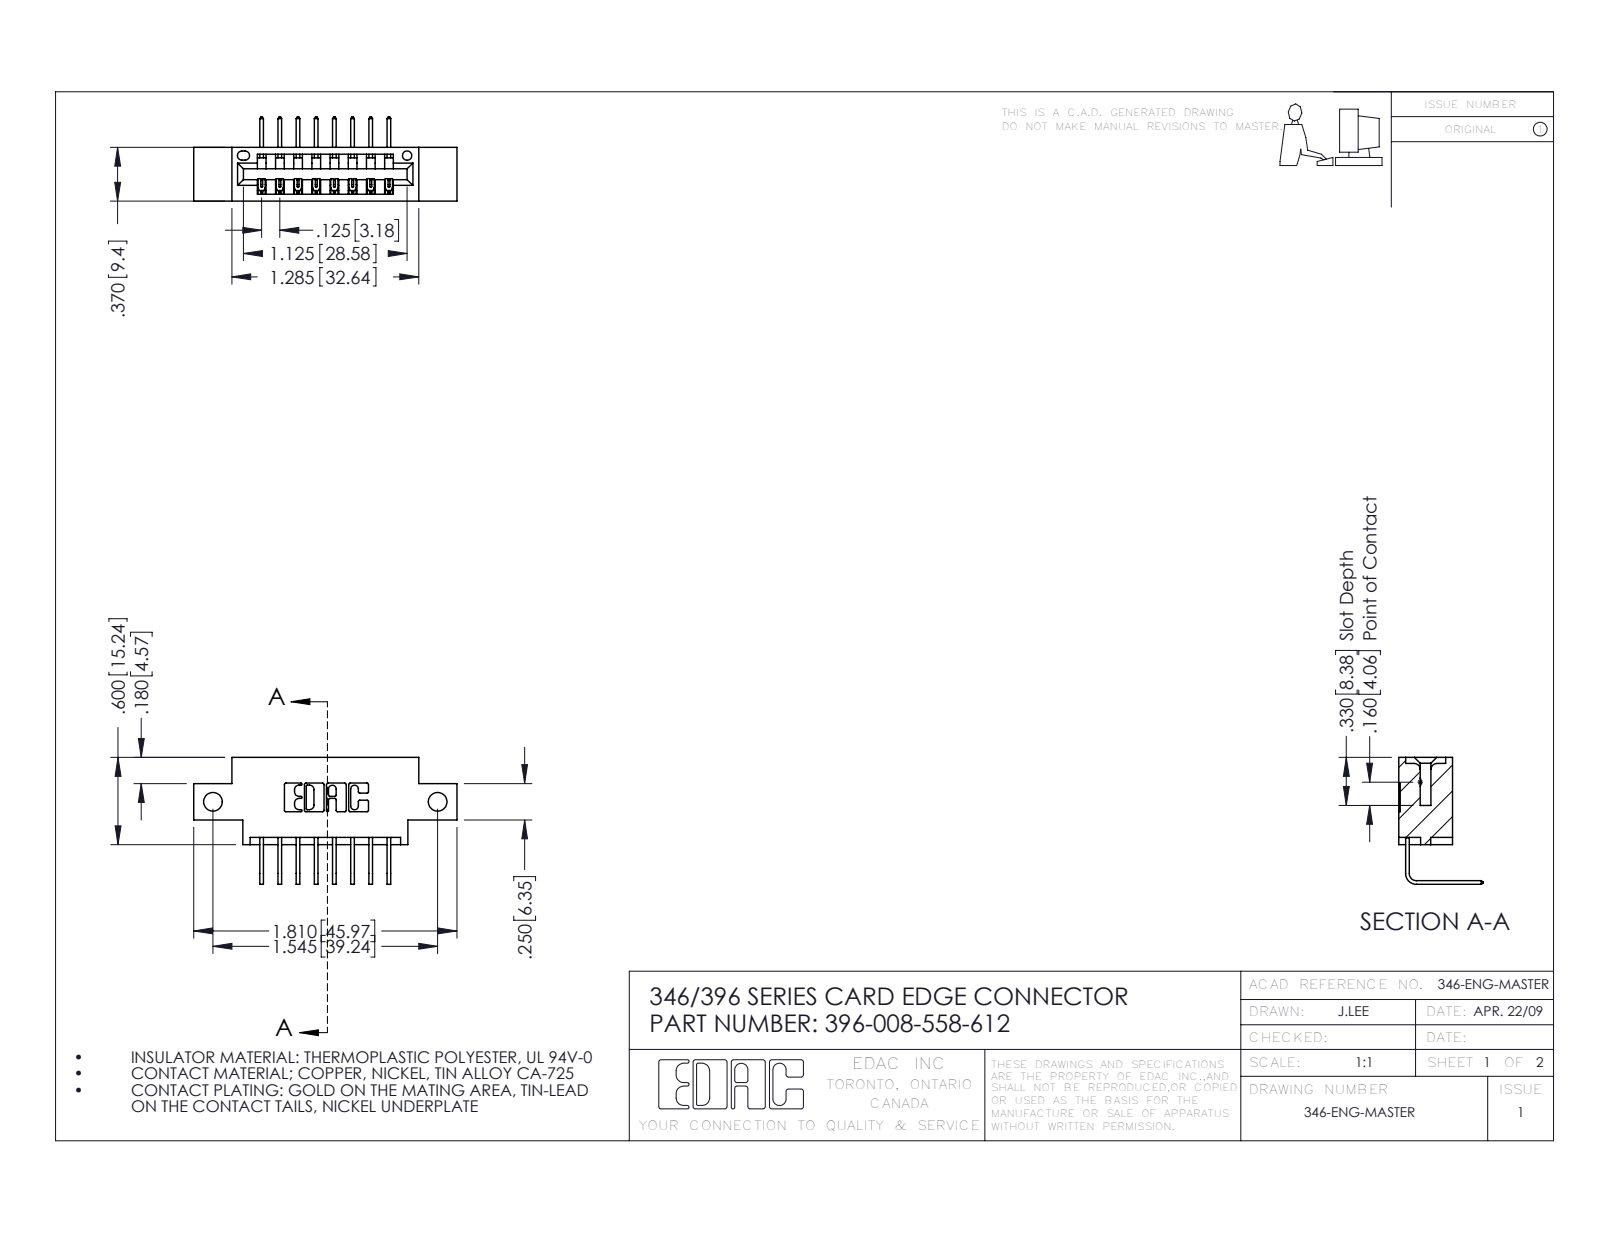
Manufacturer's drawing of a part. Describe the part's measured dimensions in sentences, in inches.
The part is named "346 Part_0.170 Offset - Side Mount; 345-292-001_558 Tail - 2; 396-008-558-612". Its 3-D file was written by "SolidWorks 2016 (CONFIG_CONTROL_DESIGN)". It is 9 solids with 606 faces: 416 planar, 190 cylindrical and 0 other. Overall it measures 1.81 by 0.873 by 0.58 inches. Its volume is 0.241 cubic inches and its surface area 7.355 square inches. Round holes: 2 of diameter 0.128, 1 of diameter 0.064. Partial cylindrical surfaces (rounded edges, fillets, slot ends): 22 of radius 0.01, 16 of radius 0.006, 6 of radius 0.007, 6 of radius 0.031, 3 of radius 0.026, 2 of radius 0.031, 2 of radius 0.04, 1 of radius 0.014. The main face-to-face distances are 0.25, 0.37, 0.322, 0.048, 0.298, 0.025, 0.148, 0.222, 0.1, 0.174. The hole center spacings are 1.545.
